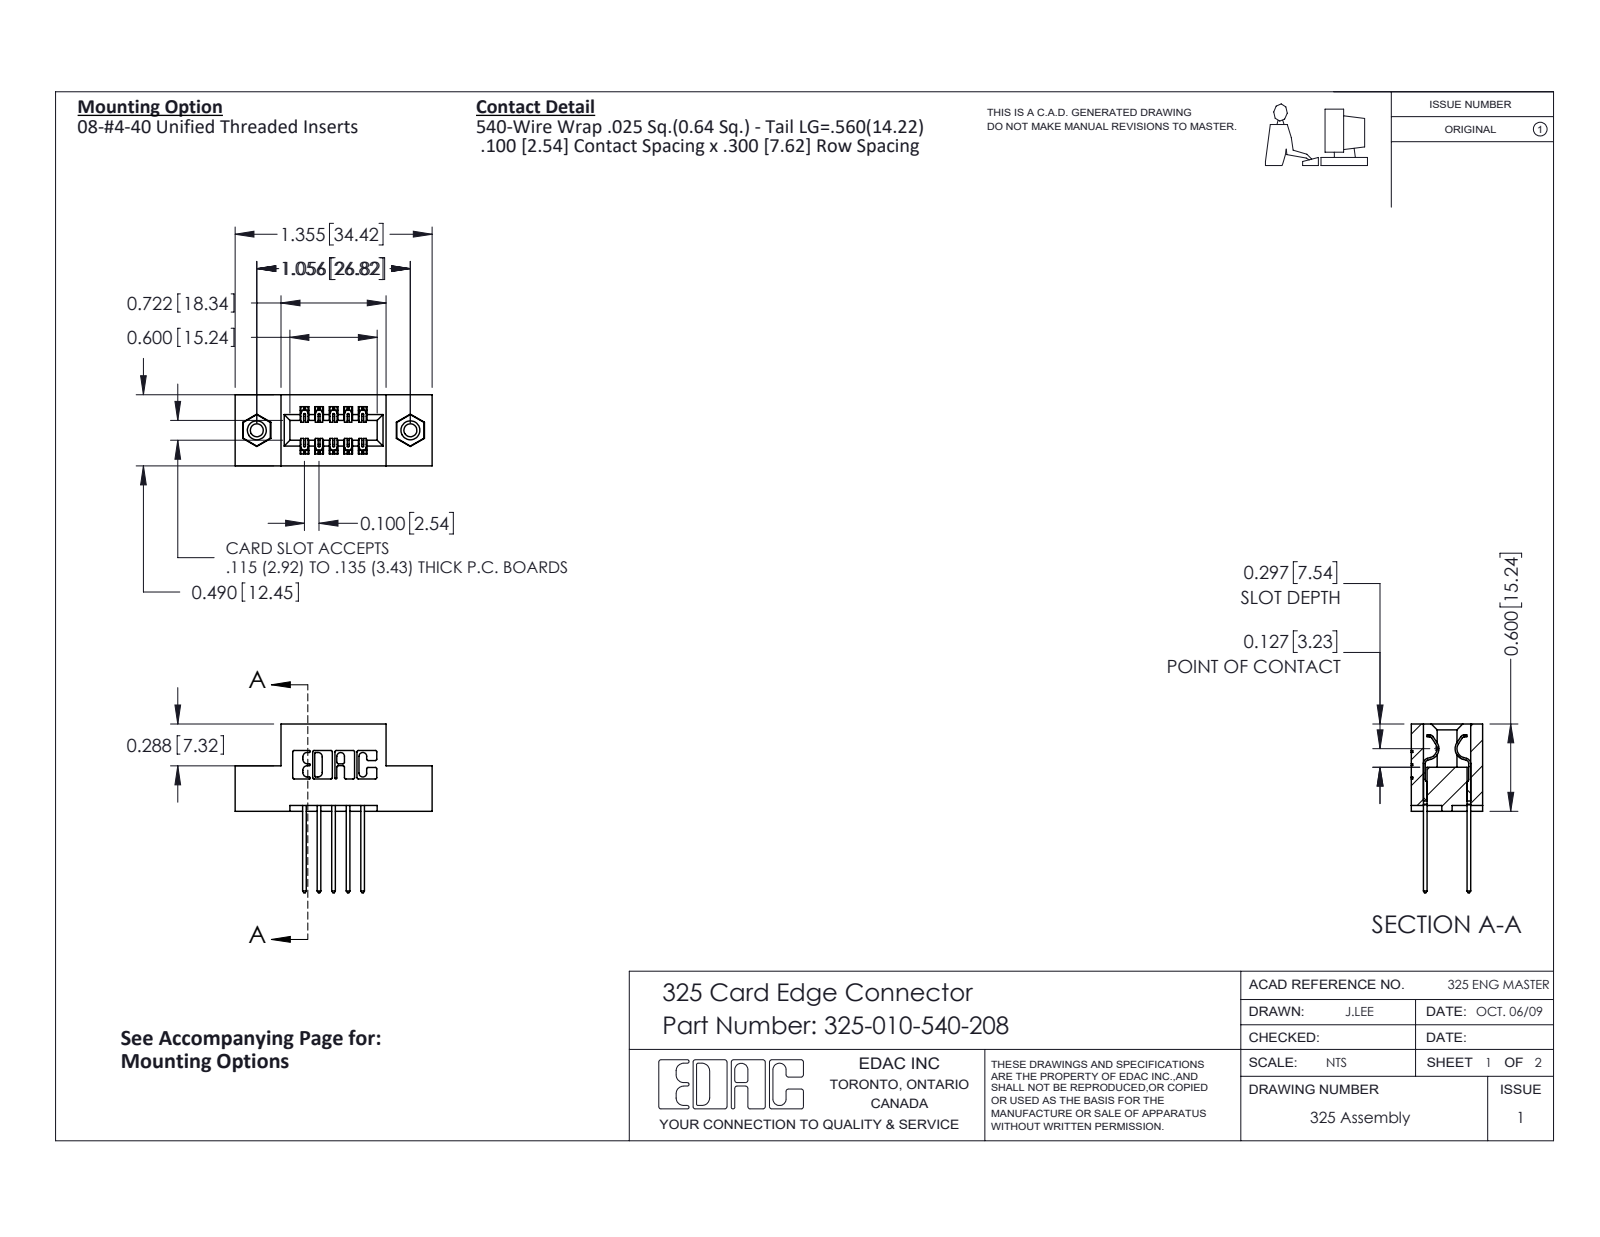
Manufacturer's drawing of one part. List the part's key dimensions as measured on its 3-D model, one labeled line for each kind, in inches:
Part name (STEP PRODUCT): 345-250-001_345-250-003-102; 325-010-540-208; 325 Part_TI; 325-292-001_325-293-140
STEP written by: SolidWorks 2016 (CONFIG_CONTROL_DESIGN)
Units: inches
Bodies: 13 solids, 694 faces (462 planar, 216 cylindrical, 16 other)
Overall size (bounding box): 1.355 × 1.16 × 0.49
Volume: 0.253 in³ · Surface area: 6.712 in²
Round holes (diameter × count): ⌀0.089 ×2, ⌀0.125 ×2, ⌀0.16 ×2
Round bosses / shafts (diameter × count): ⌀0.155 ×2
Partial cylindrical surfaces — rounded edges, fillets, slot ends (radius × count): R0.01 ×22, R0.006 ×15, R0.01 ×10, R0.007 ×6, R0.031 ×6, R0.026 ×3, R0.014 ×2, R0.022 ×2
Main face-to-face distances: 0.083, 0.3, 0.407, 0.1, 0.49, 0.04, 0.2, 0.383, 0.107, 0.025
Hole centre spacings: 1.056
